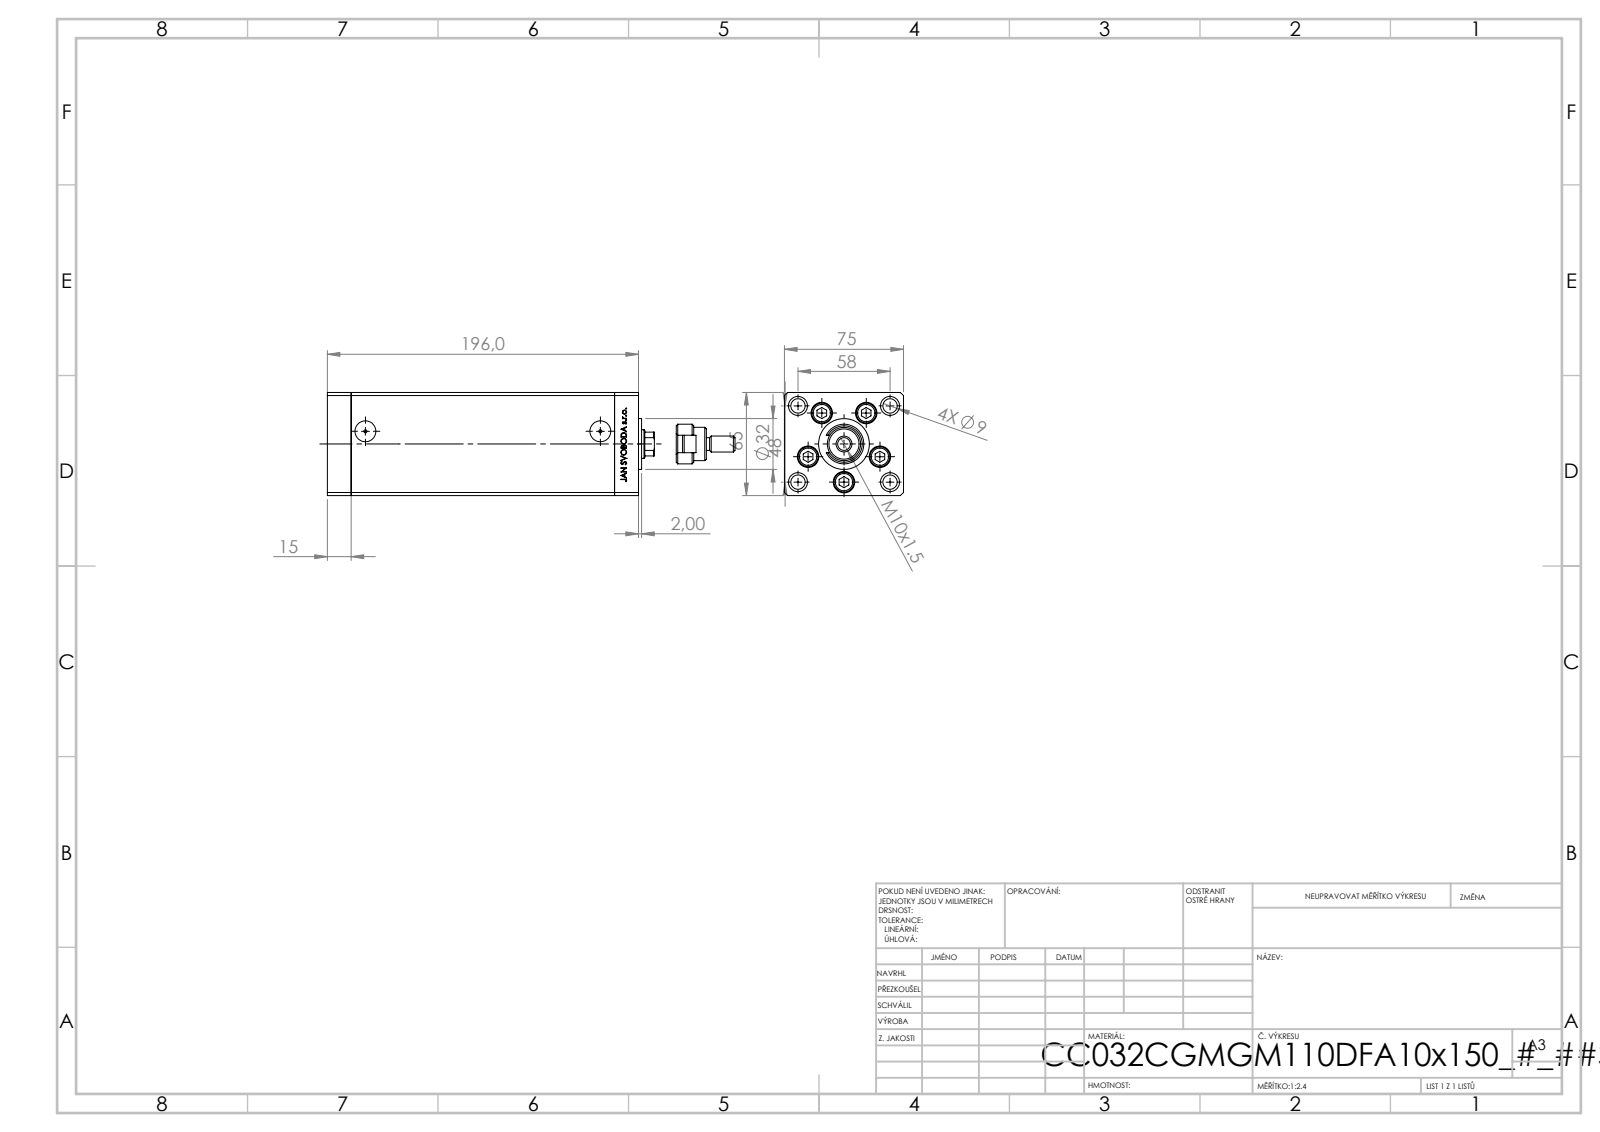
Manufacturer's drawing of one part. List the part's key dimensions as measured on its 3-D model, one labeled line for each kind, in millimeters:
Part name (STEP PRODUCT): V220C_C MIDDLE; ALLEN BOLT; V220C FRONT; V220C BACK_C (+2 more)
STEP written by: SolidWorks 2019 (CONFIG_CONTROL_DESIGN)
Units: millimetres
Bodies: 14 solids, 1206 faces (556 planar, 176 cylindrical, 474 other)
Overall size (bounding box): 256.8 × 75 × 65
Volume: 803 462 mm³ · Surface area: 163 274 mm²
Round holes (diameter × count): ⌀9 ×9, ⌀13.5 ×5, ⌀8 ×4, ⌀12 ×4, ⌀2 ×2, ⌀13.16 ×2, ⌀8.5 ×1, ⌀12.5 ×1, ⌀18 ×1
Round bosses / shafts (diameter × count): ⌀8 ×6, ⌀12.5 ×4, ⌀32 ×1, ⌀25 ×1, ⌀21 ×1, ⌀10 ×1
Partial cylindrical surfaces — rounded edges, fillets, slot ends (radius × count): R0.93 ×2, R5.5 ×1, R8.5 ×1, R8.75 ×1
Main face-to-face distances: 75, 65, 15, 166, 181, 196, 54.5, 10.5, 13, 28
Hole centre spacings: 24, 37.64, 15.67, 17.22, 27.71, 28.83, 29, 32.63
